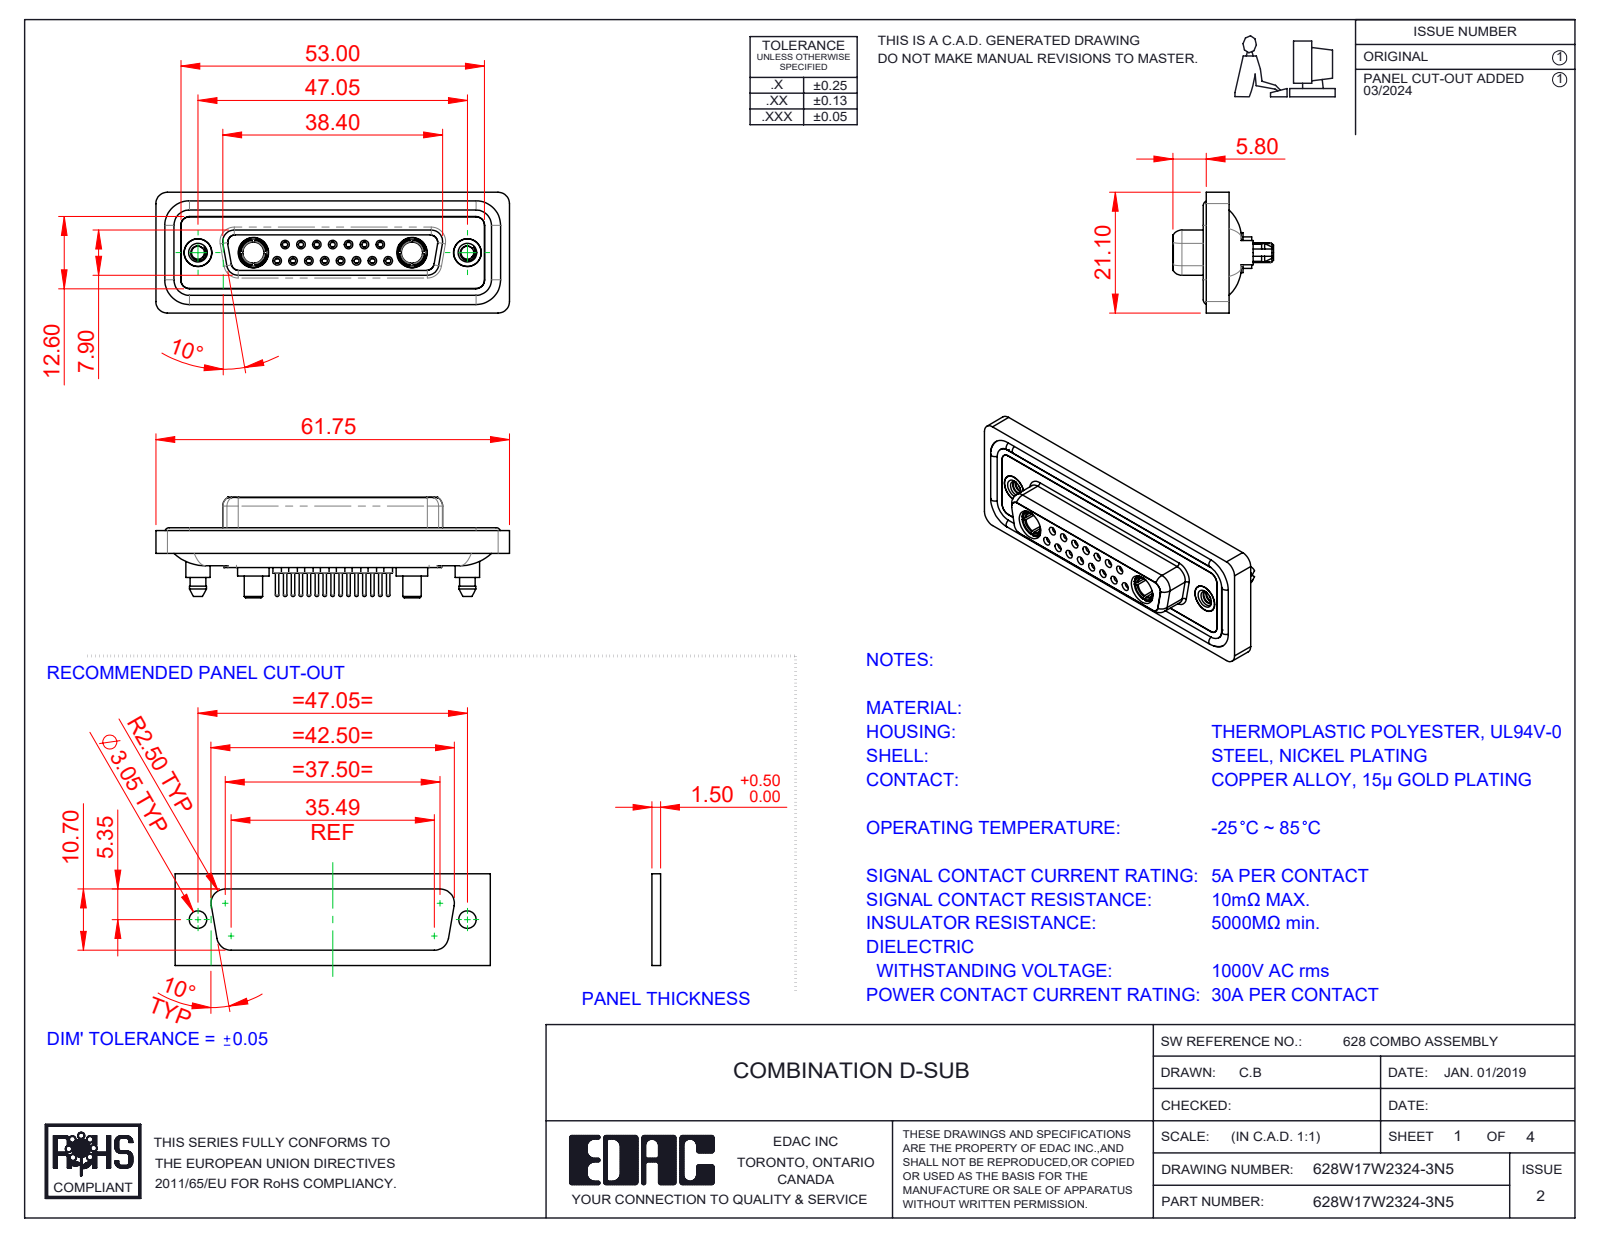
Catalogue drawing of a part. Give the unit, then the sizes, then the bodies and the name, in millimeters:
Units: millimetres
Overall size (bounding box): 61.75 × 21.1 × 17.55
Round holes (diameter × count): ⌀0.9 ×15, ⌀1.1 ×15, ⌀1.5 ×15, ⌀2 ×15, ⌀1.6 ×8, ⌀1.7 ×7, ⌀4.85 ×4, ⌀2.26 ×2, ⌀3.7 ×2, ⌀4 ×2, ⌀4.05 ×2, ⌀5 ×2
Round bosses / shafts (diameter × count): ⌀2.2 ×15, ⌀0.6 ×15, ⌀1.6 ×11, ⌀5.5 ×2, ⌀5.4 ×2, ⌀5.2 ×2, ⌀4.96 ×2, ⌀4.95 ×2
Partial cylindrical surfaces — rounded edges, fillets, slot ends (radius × count): R1.5 ×24, R2 ×18, R1.6 ×10, R1.35 ×8, R0.25 ×4, R0.5 ×4, R0.6 ×4, R0.65 ×4
Main face-to-face distances: 0.4, 1.8, 7.45, 5.65, 6.6, 0.5, 7.05, 1.6, 2.9, 1.1
Hole centre spacings: 3.16, 2.77, 8.31, 5.54, 5.03, 5.04, 7.49, 11.08
Volume: 8 472 mm³ · Surface area: 14 197 mm²
Bodies: 26 solids, 1409 faces (404 planar, 551 cylindrical, 454 other)
Part name (STEP PRODUCT): 628Combo Shell Front_25 Contacts; 628Combo Waterproof Housing_25 Contacts; 628Combo Shell Rear_25 Contacts; 628W17W2324-3N5 (+5 more)
STEP written by: SolidWorks 2023 (CONFIG_CONTROL_DESIGN)
